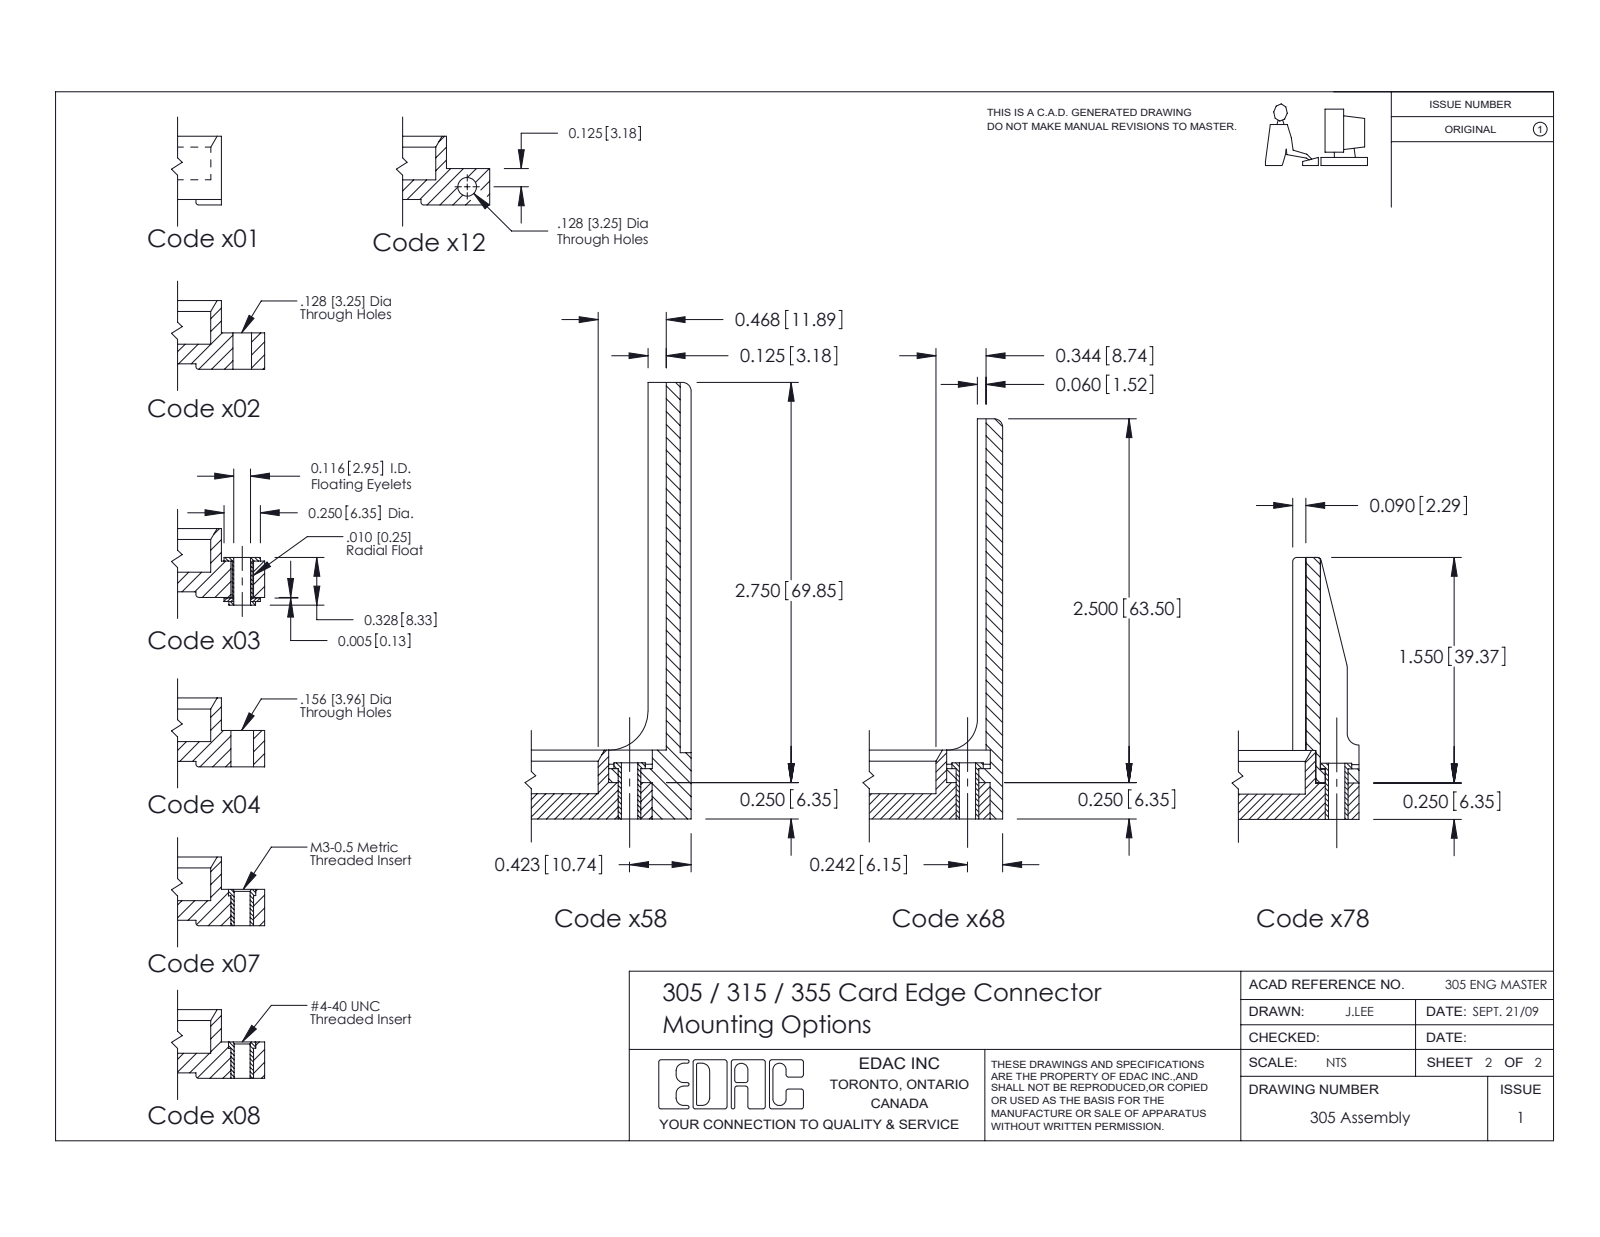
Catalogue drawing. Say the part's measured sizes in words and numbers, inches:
The part is named "305-290-001_500; 315-026-500-212; 305 Part_.128 Dia". Its 3-D file was written by "SolidWorks 2020 (CONFIG_CONTROL_DESIGN)". It is 27 solids with 1428 faces: 796 planar, 580 cylindrical and 52 other. Overall it measures 2.934 by 0.742 by 0.343 inches. Its volume is 0.283 cubic inches and its surface area 13.44 square inches. Round holes: 4 of diameter 0.128. Partial cylindrical surfaces (rounded edges, fillets, slot ends): 45 of radius 0.015, 26 of radius 0.023, 26 of radius 0.03, 22 of radius 0.01, 13 of radius 0.006, 6 of radius 0.007, 6 of radius 0.031, 3 of radius 0.026. The main face-to-face distances are 0.013, 0.176, 0.037, 0.343, 0.05, 0.058, 0.284, 0.226, 0.285, 0.059. The hole center spacings are 2.624.
